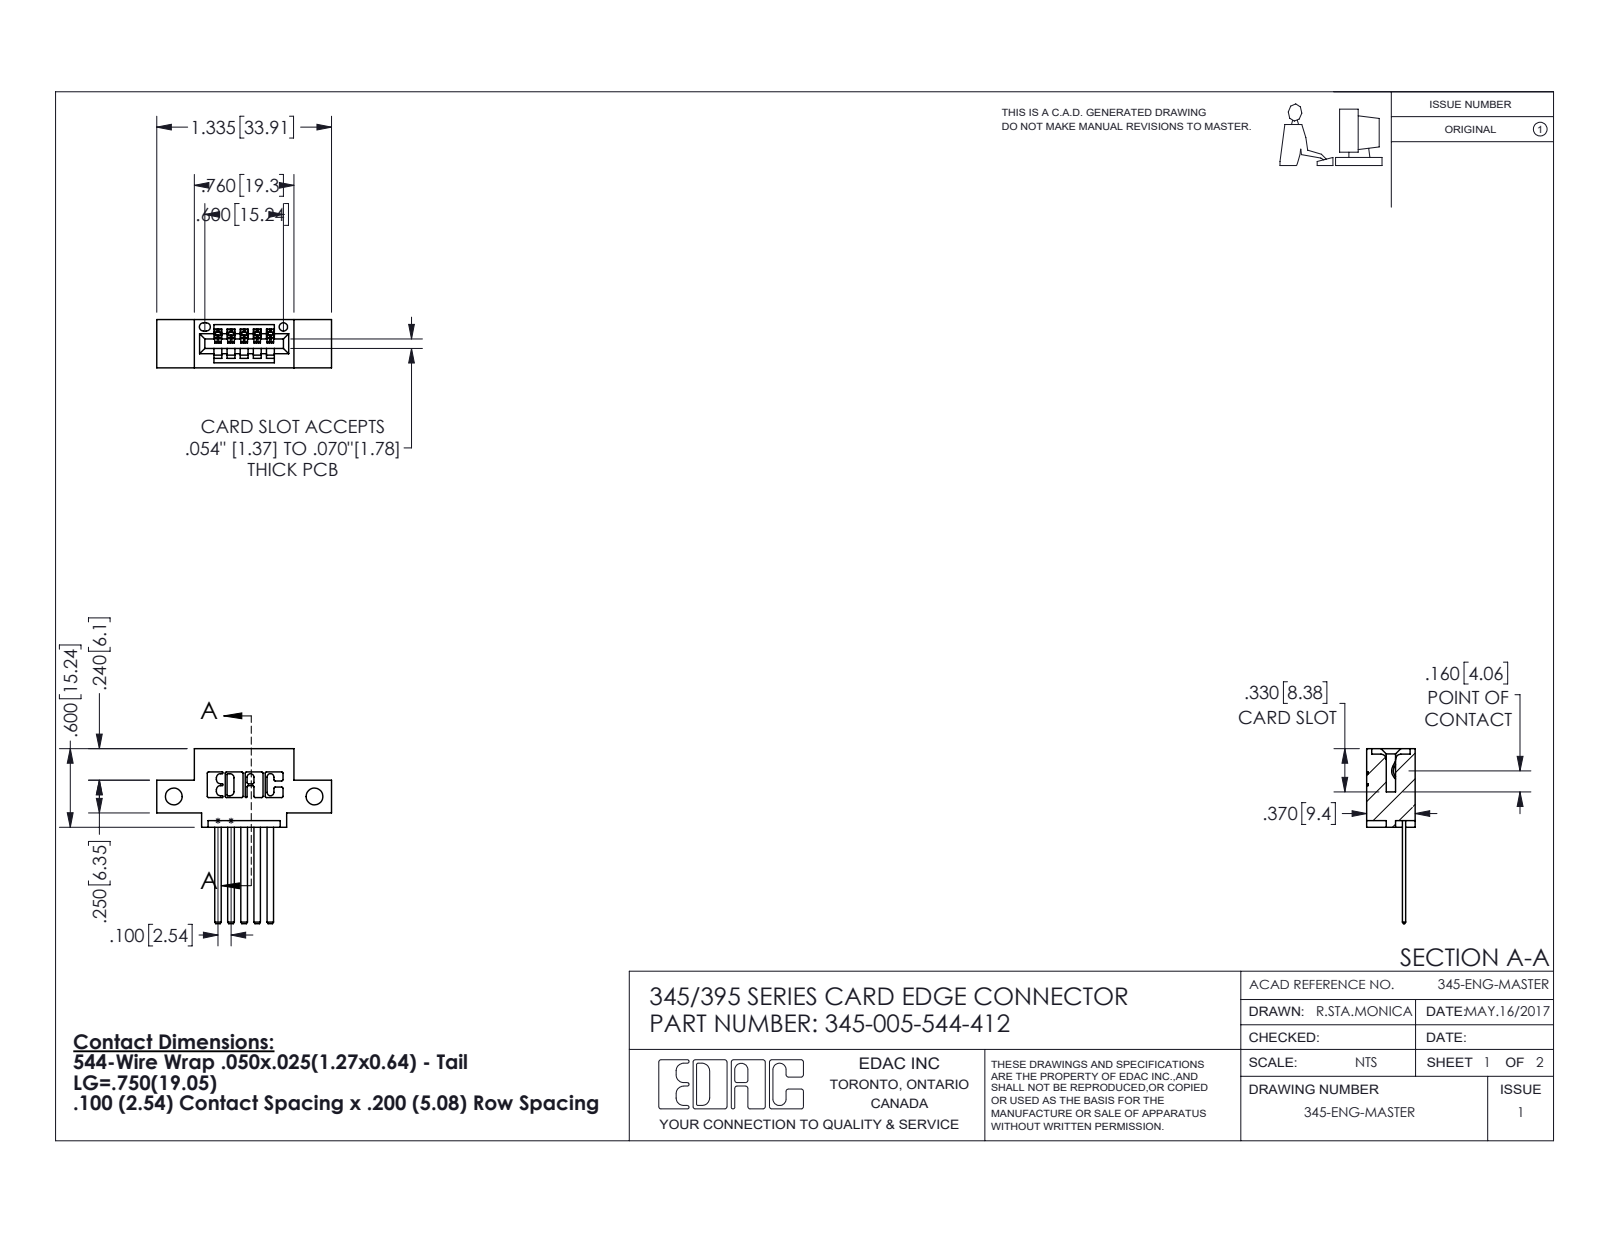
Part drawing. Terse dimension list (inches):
name: 345-292-001_345-293-144; 345-005-544-412; 345 Part_0.110 Offset - Side Mount
written by: SolidWorks 2016 (CONFIG_CONTROL_DESIGN)
unit: in
bodies: 6 solids, 390 faces (264 planar, 126 cylindrical, 0 other)
size: 1.337 × 1.335 × 0.37
volume: 0.172 in³; area: 5.195 in²
holes: 2× ⌀0.128, 1× ⌀0.064
rounds: 22× R0.01, 10× R0.006, 6× R0.007, 6× R0.031, 3× R0.026, 2× R0.031, 2× R0.04, 1× R0.014
face distances: 0.298, 0.072, 0.2, 0.37, 0.1, 0.25, 0.098, 0.272, 0.025, 0.15
hole spacings: 1.075
